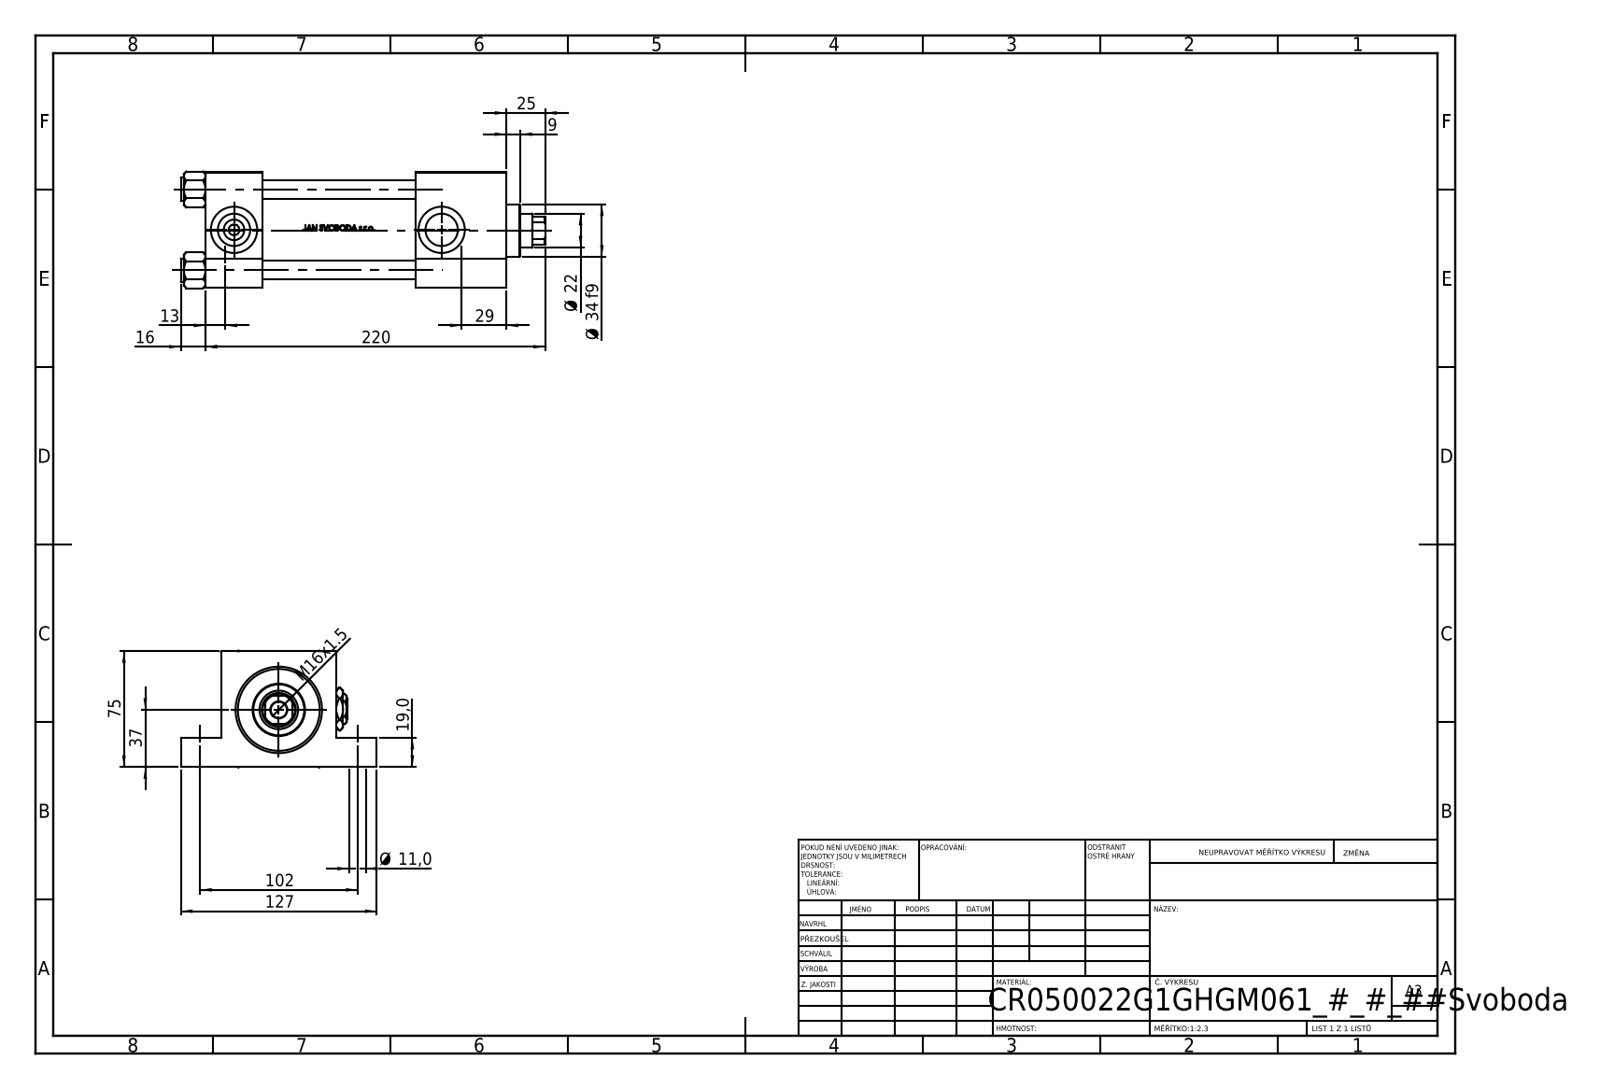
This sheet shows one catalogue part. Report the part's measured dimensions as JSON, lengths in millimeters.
{"part_name": "V215CR_G_Body; Zatka_pro_OIL_PORT; NUT_M5_G; V215CR_G_TYCINKA (+2 more)", "step_written_by": "SolidWorks 2019 (CONFIG_CONTROL_DESIGN)", "units": "millimeters", "bodies": {"solids": 12, "faces": 1134, "planar": 454, "cylindrical": 128, "other": 552}, "overall_size": [236, 127, 75.54], "volume_mm3": 807017, "surface_area_mm2": 183973, "round_holes": [[11, 4], [12, 4], [7, 2], [20.96, 2], [30, 2], [10.5, 1], [22, 1], [25, 1], [41, 1], [50, 1], [53, 1]], "round_bosses_or_shafts": [[15, 4], [56, 1], [34, 1]], "partial_cylinders_radius": [[10.5, 1]], "face_to_face_distances": [75, 37, 195, 158, 19, 56, 136, 99, 59, 26], "hole_center_spacings": [52.3, 36.63, 37.34, 73.96, 102, 153, 183.88, 134.5]}
